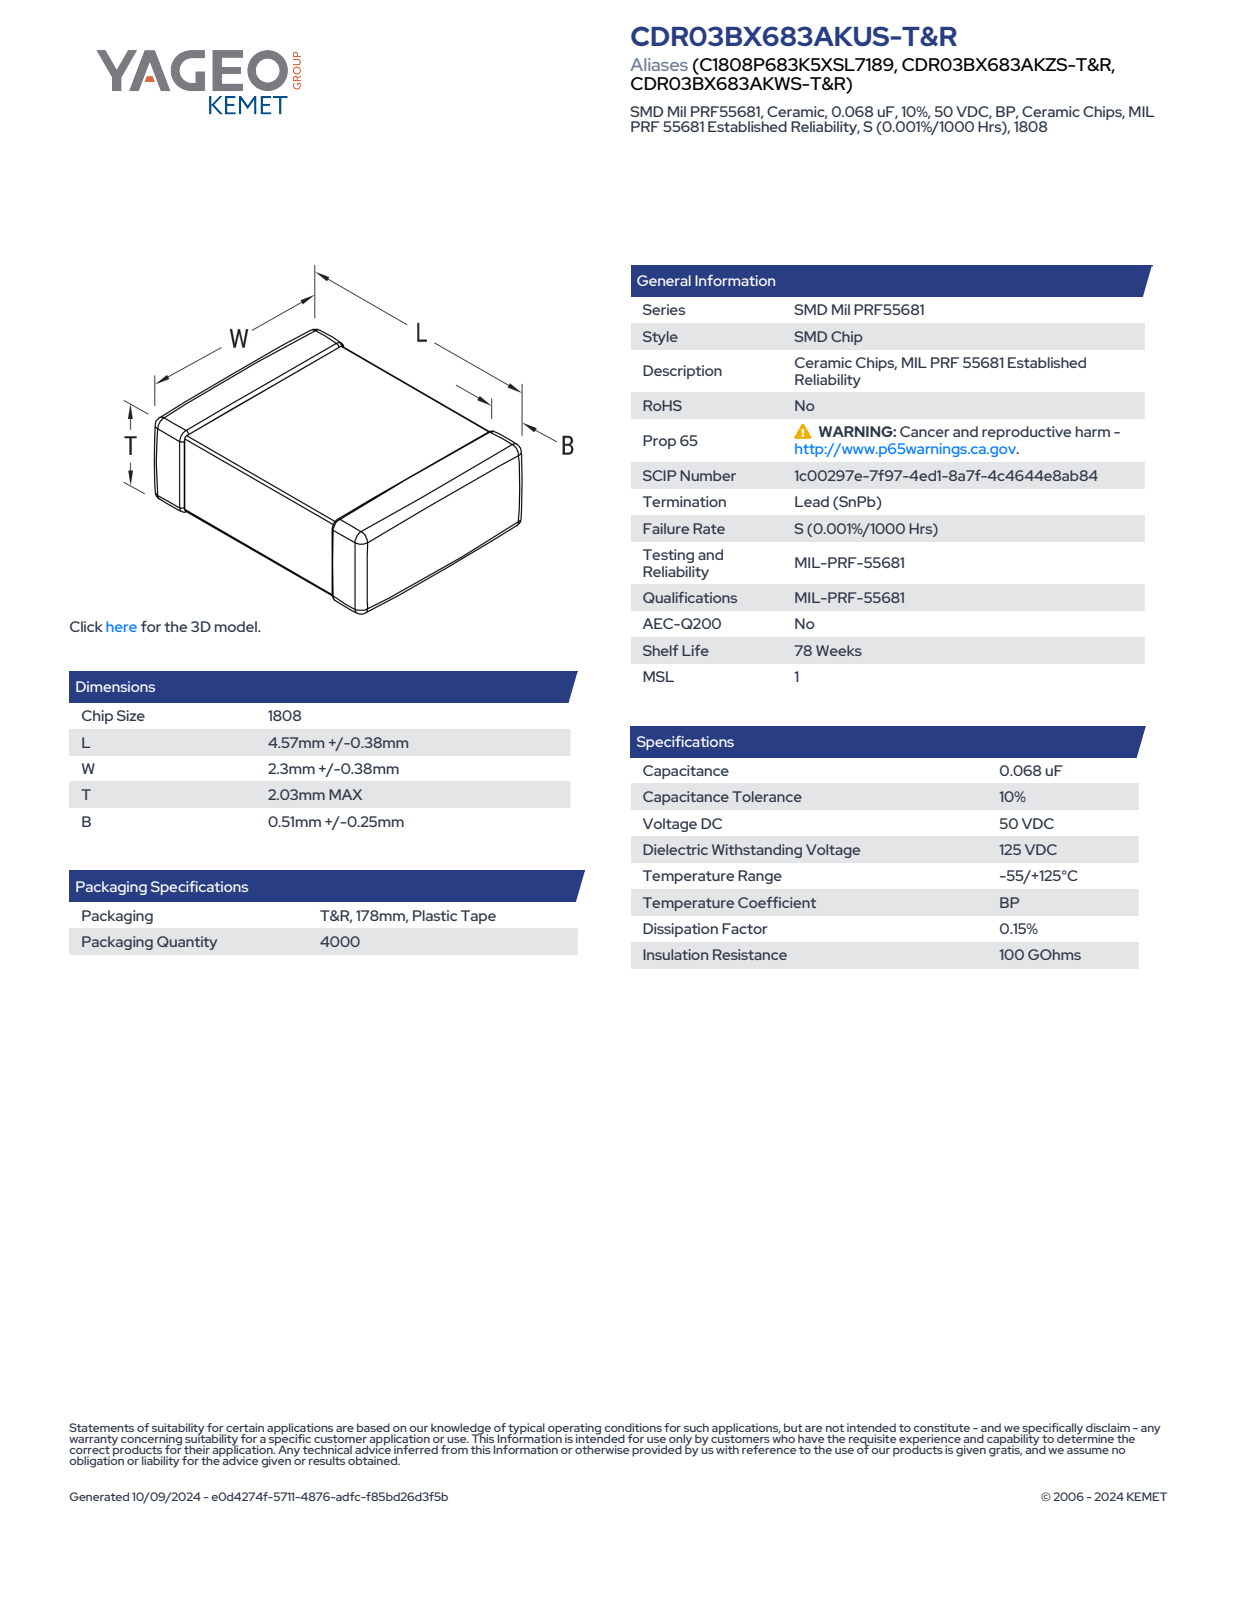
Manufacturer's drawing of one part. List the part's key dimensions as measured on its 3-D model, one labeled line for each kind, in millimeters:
Part name (STEP PRODUCT): CCS_STDNOS_1808_L4.95W2.68T2.03B0.76
STEP written by: SolidWorks 2021 (AUTOMOTIVE_DESIGN)
Units: millimetres
Bodies: 4 solids, 125 faces (71 planar, 38 cylindrical, 16 other)
Overall size (bounding box): 4.95 × 2.68 × 2.03
Volume: 25 mm³ · Surface area: 56 mm²
Main face-to-face distances: 1.91, 1.97, 2.56, 2.62, 4.95, 2.03, 2.68, 1.98, 1.92, 1.43
